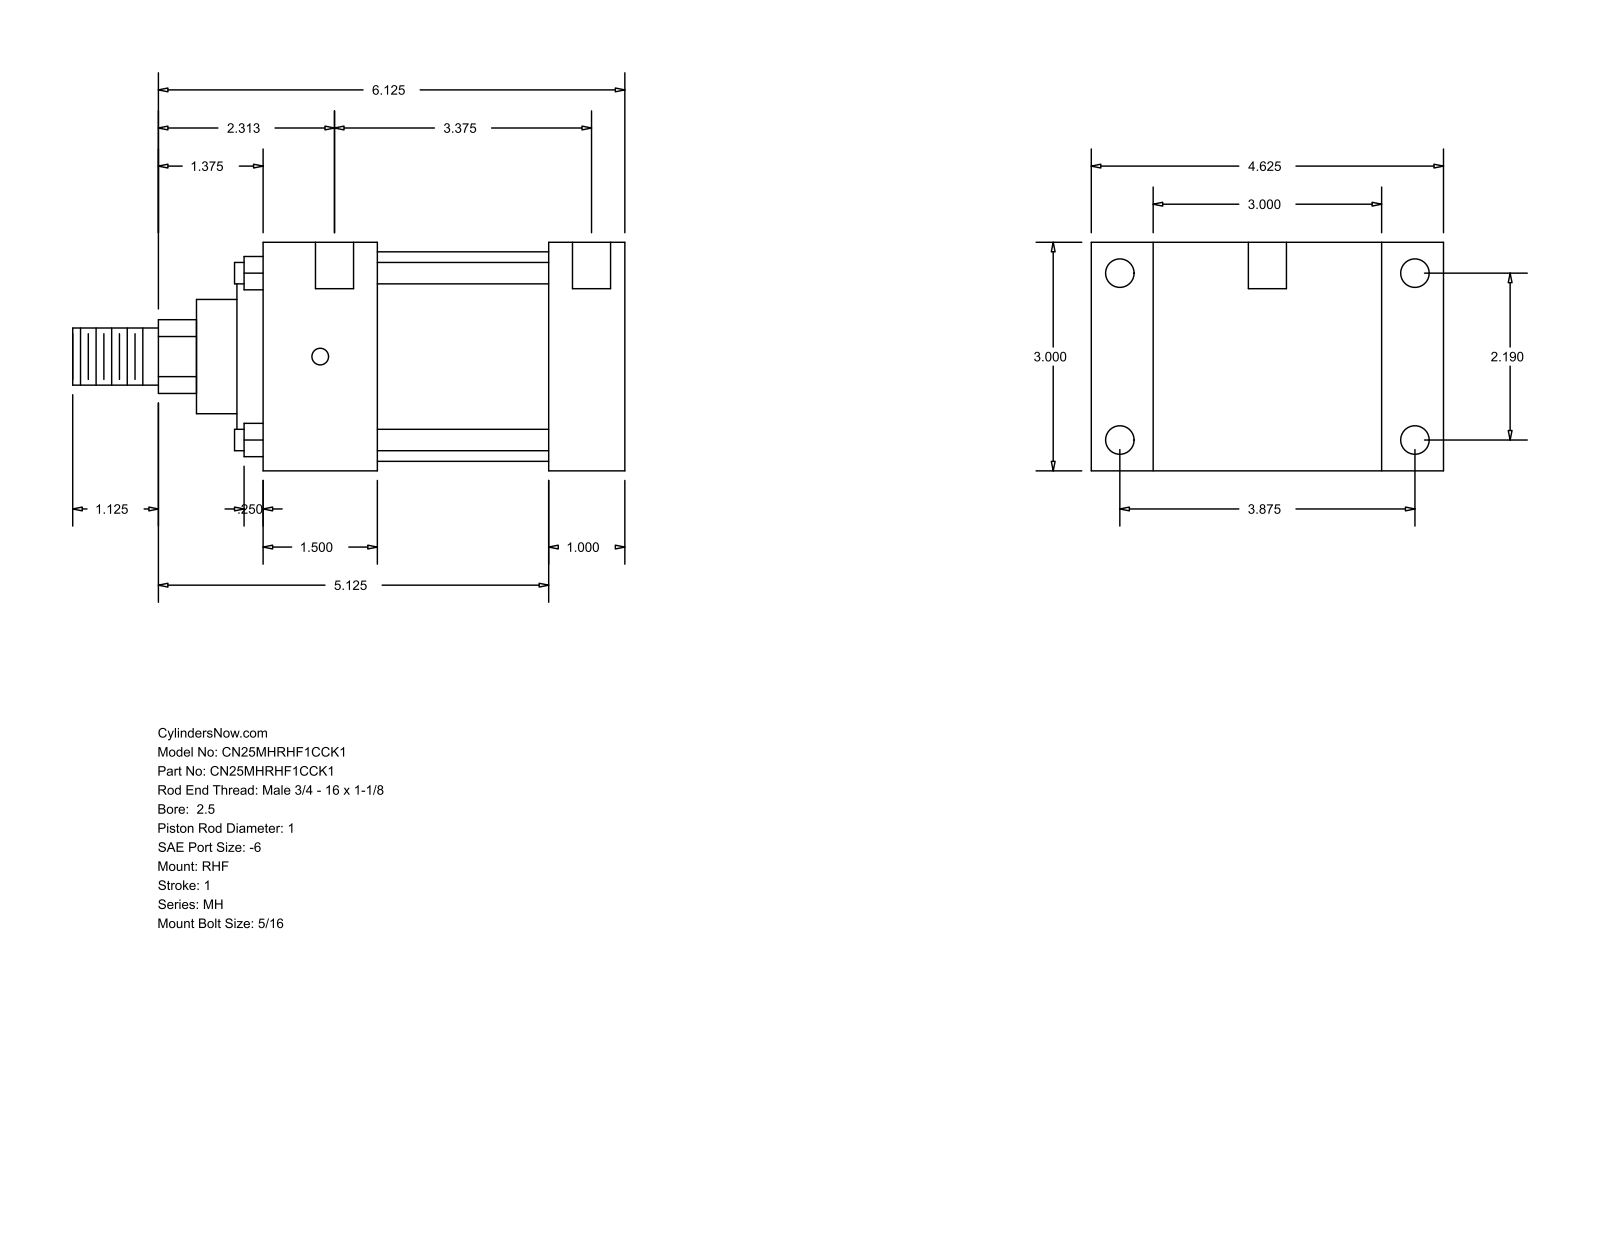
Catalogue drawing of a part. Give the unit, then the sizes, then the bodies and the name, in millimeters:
Units: millimetres
Overall size (bounding box): 184.15 × 117.47 × 76.2
Round holes (diameter × count): ⌀5.56 ×4, ⌀9.53 ×4, ⌀12.7 ×2
Round bosses / shafts (diameter × count): ⌀7.14 ×4, ⌀69.85 ×1, ⌀60.33 ×1, ⌀38.1 ×1, ⌀25.4 ×1, ⌀19.05 ×1
Partial cylindrical surfaces — rounded edges, fillets, slot ends (radius × count): R12.29 ×1
Main face-to-face distances: 76.2, 25.39, 20.64, 96.84, 120.65, 117.48, 95.26, 38.11, 57.15, 82.54
Hole centre spacings: 55.62, 93.66, 98.42, 113.05, 3.18, 4.76, 85.72, 88.9
Bodies: 0 solids, 90 faces (61 planar, 29 cylindrical, 0 other)
Part name (STEP PRODUCT): MH_RHF__0250_1
STEP written by: GSSL Pune (CONFIG_CONTROL_DESIGN)
